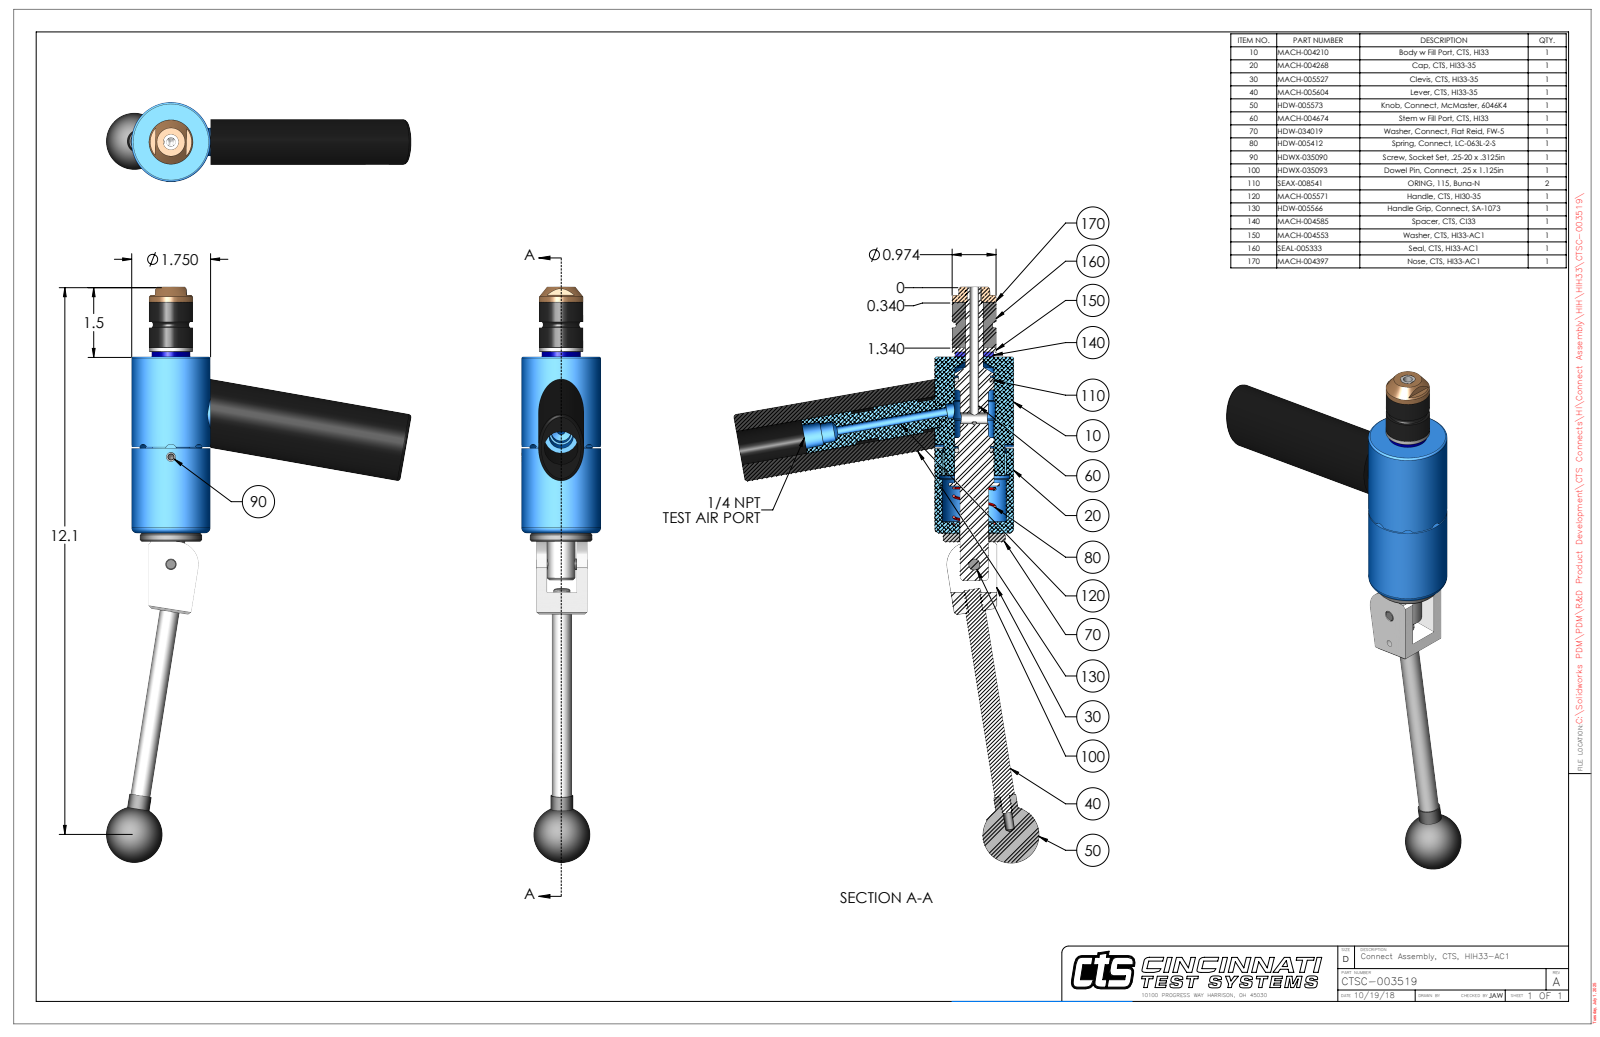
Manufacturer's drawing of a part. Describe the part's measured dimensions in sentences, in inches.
The part is named "CTSC-003519". Its 3-D file was written by "SolidWorks 2023 (AUTOMOTIVE_DESIGN)". It is 11 solids with 288 faces: 93 planar, 126 cylindrical and 69 other. Overall it measures 12.751 by 6.763 by 1.75 inches. Its volume is 17.8 cubic inches and its surface area 111.8 square inches. Round holes: 2 of diameter 0.201, 2 of diameter 0.313, 1 of diameter 0.15, 1 of diameter 0.187, 1 of diameter 0.204, 1 of diameter 0.249, 1 of diameter 0.25, 1 of diameter 0.251, 1 of diameter 0.39, 1 of diameter 0.397, 1 of diameter 0.403, 1 of diameter 0.438. Round bosses or shafts: 2 of diameter 0.375, 2 of diameter 0.312, 2 of diameter 0.25, 1 of diameter 1.75, 1 of diameter 1.38, 1 of diameter 0.974, 1 of diameter 0.858, 1 of diameter 0.75. Partial cylindrical surfaces (rounded edges, fillets, slot ends): 4 of radius 0.125, 2 of radius 0.029, 1 of radius 0.143, 1 of radius 0.33, 1 of radius 0.5, 1 of radius 0.695, 1 of radius 0.829. The main face-to-face distances are 3.907, 1.12, 1.207, 5.114, 1, 5.302, 4.095, 0.188, 0.207, 4.114. The hole center spacings are 0.74, 2.376, 3.116.
